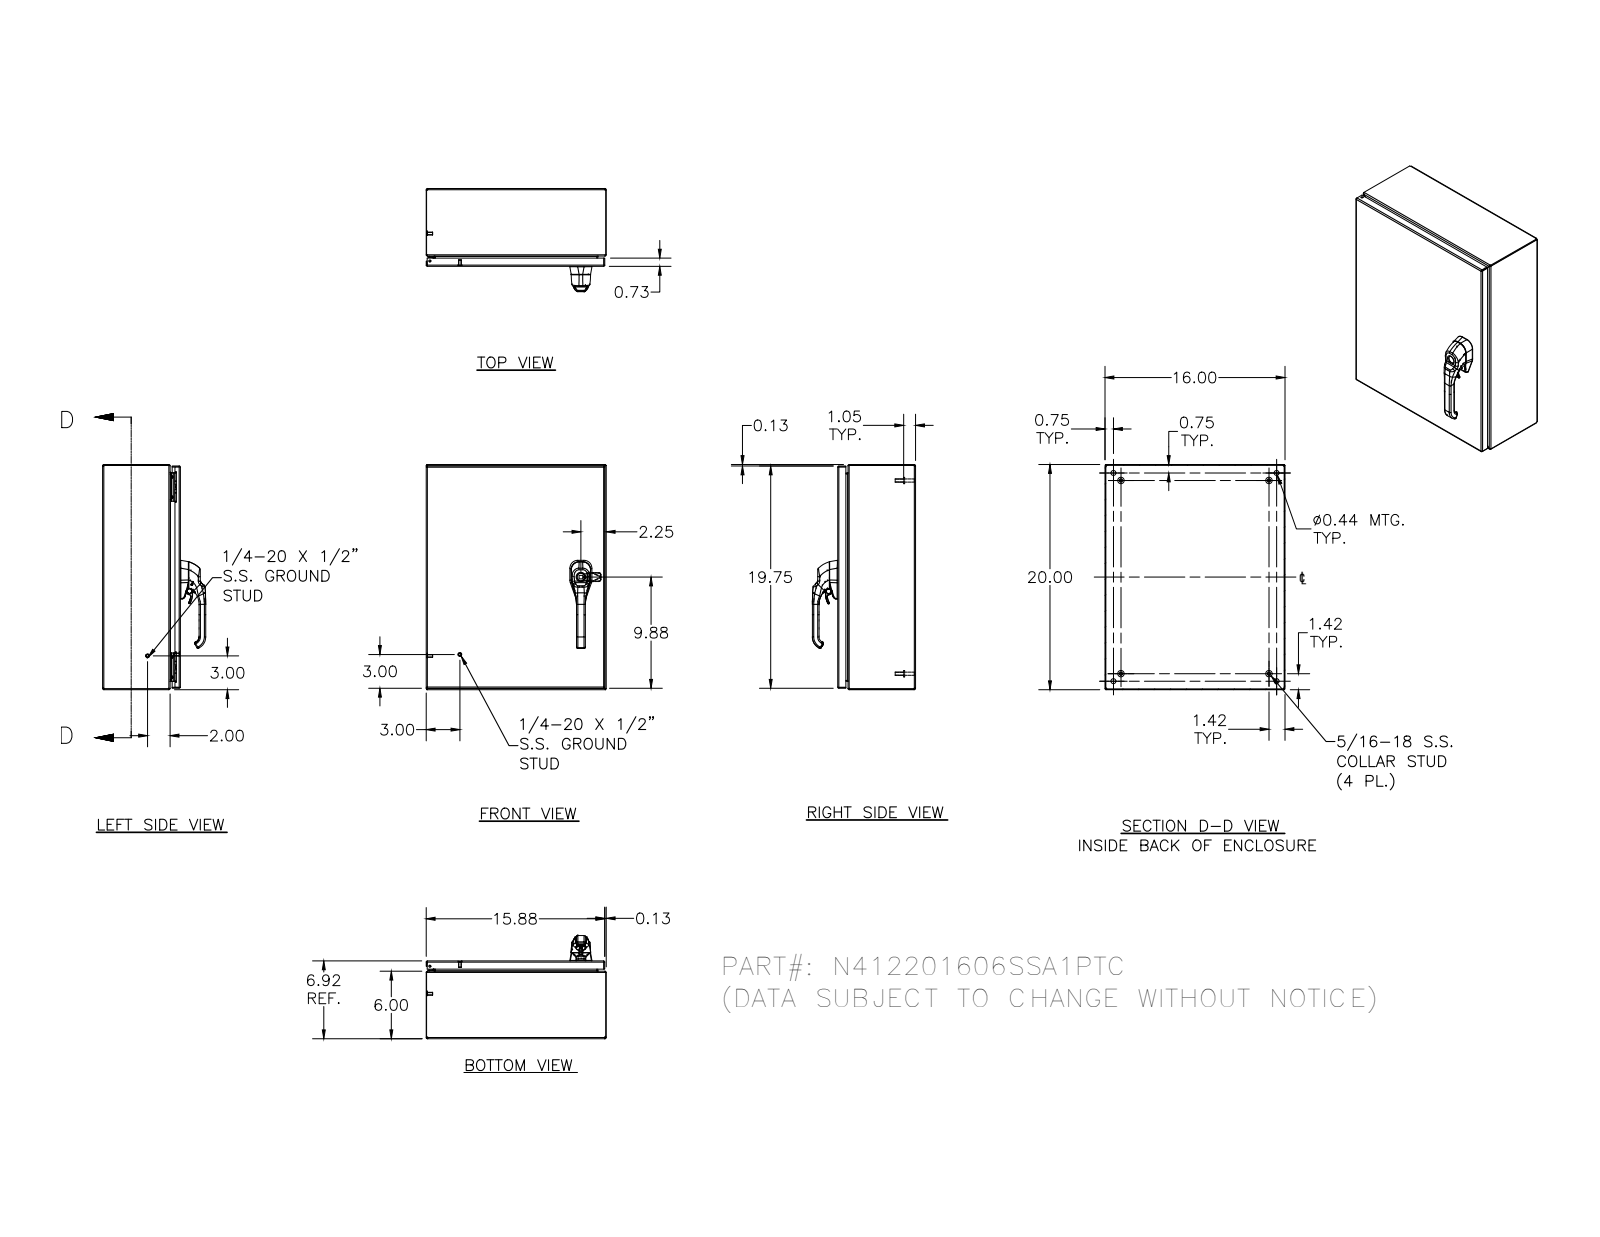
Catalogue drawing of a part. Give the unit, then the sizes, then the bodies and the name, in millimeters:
Units: millimetres
Overall size (bounding box): 508 × 406.4 × 232.8
Round holes (diameter × count): ⌀4.8 ×5, ⌀2.4 ×4, ⌀3.9 ×4, ⌀4.2 ×4, ⌀4.4 ×4, ⌀11.1 ×4, ⌀5.4 ×3, ⌀7.1 ×3, ⌀4 ×2, ⌀8 ×2, ⌀10.2 ×2, ⌀10.5 ×2
Round bosses / shafts (diameter × count): ⌀6.4 ×10, ⌀14.3 ×4, ⌀9.1 ×4, ⌀8.1 ×4, ⌀7.6 ×4, ⌀7 ×4, ⌀6.5 ×4, ⌀4.2 ×4
Partial cylindrical surfaces — rounded edges, fillets, slot ends (radius × count): R0.5 ×174, R0.3 ×101, R0.8 ×30, R1.3 ×26, R0.5 ×21, R2.7 ×20, R0.4 ×18, R2 ×14
Main face-to-face distances: 1.9, 173.8, 175.7, 171.9, 404.5, 506.1, 402.6, 406.4, 508, 504.2
Hole centre spacings: 406.3, 0.4, 16.8, 388.2, 406.5, 423.1, 0.5, 12.7
Volume: 1 595 000 mm³ · Surface area: 1 645 000 mm²
Bodies: 41 solids, 2784 faces (882 planar, 1037 cylindrical, 865 other)
Part name (STEP PRODUCT): N412201606SSA1PTC; N412201606SSA1PTCBKP; N4122016SSA1PTCLID; HFW328176 (+8 more)
STEP written by: Autodesk Inventor 2012 (AUTOMOTIVE_DESIGN)
